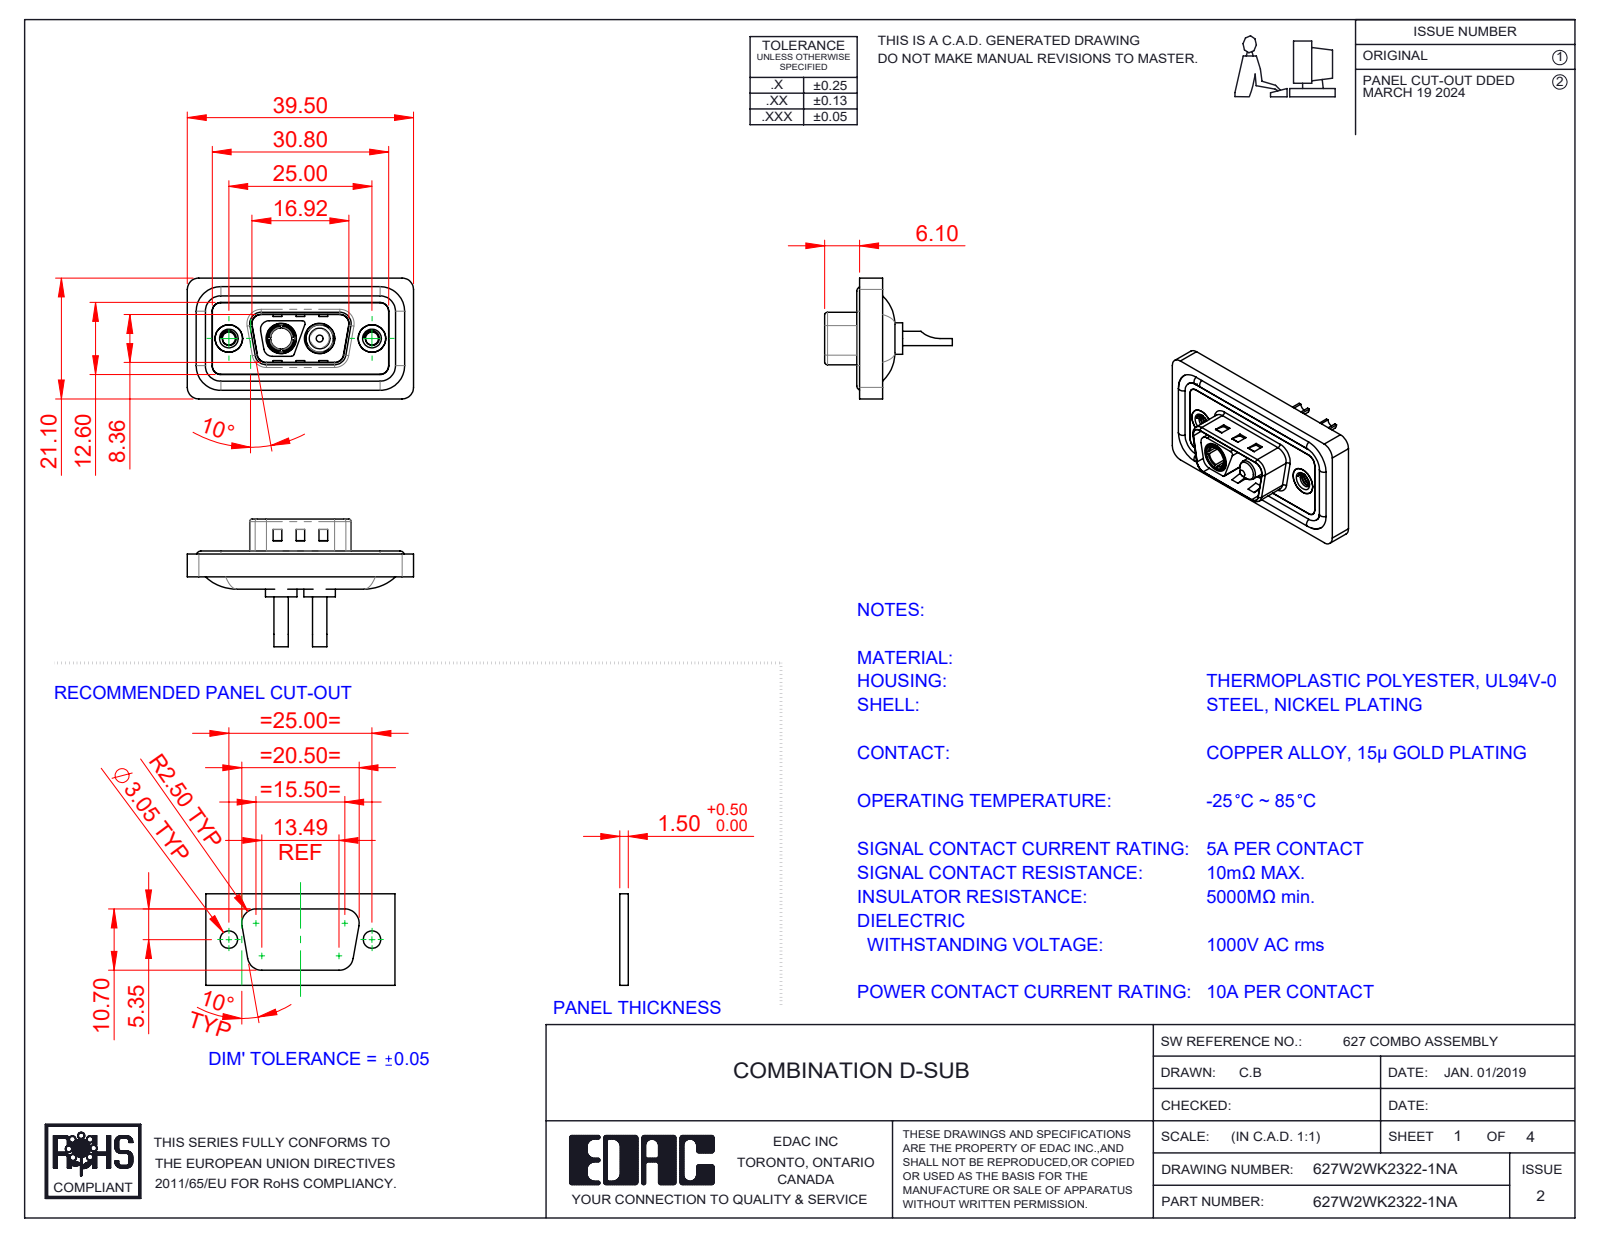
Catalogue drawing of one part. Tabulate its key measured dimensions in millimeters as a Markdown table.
| quantity | value |
| --- | --- |
| part name | Power Socket_10A SC; 627Combo Shell Front_09 Contacts; 627Combo Waterproof Housing_09 Contacts; 627Combo Threaded Rivet_A (+4 more) |
| STEP written by | SolidWorks 2023 (CONFIG_CONTROL_DESIGN) |
| units | millimeters |
| bodies | 11 solids, 544 faces (193 planar, 235 cylindrical, 116 other) |
| overall size | 39.5 × 22.3 × 21.1 |
| volume | 4 550 mm³ |
| surface area | 7 435 mm² |
| round holes (diameter × count) | 1.7 × 2, 2.26 × 2, 4 × 2, 4.8 × 2, 4.85 × 2, 5 × 2, 5.3 × 2, 3.7 × 1 |
| round bosses / shafts (diameter × count) | 1.6 × 4, 5.5 × 2, 5.2 × 2, 4.9 × 2, 4.75 × 2, 3.75 × 2, 2.5 × 2, 4.96 × 1 |
| partial cylindrical surfaces (radius × count) | 1.5 × 24, 2 × 18, 0.5 × 10, 1.6 × 8, 0.25 × 4, 0.6 × 4, 0.65 × 4, 0.9 × 4 |
| main face-to-face distances | 0.4, 1.1, 2.9, 0.5, 3.1, 1.6, 1.5, 4, 2.5, 1.8 |
| hole center spacings | 9.14, 15.86, 6.72, 25 |
